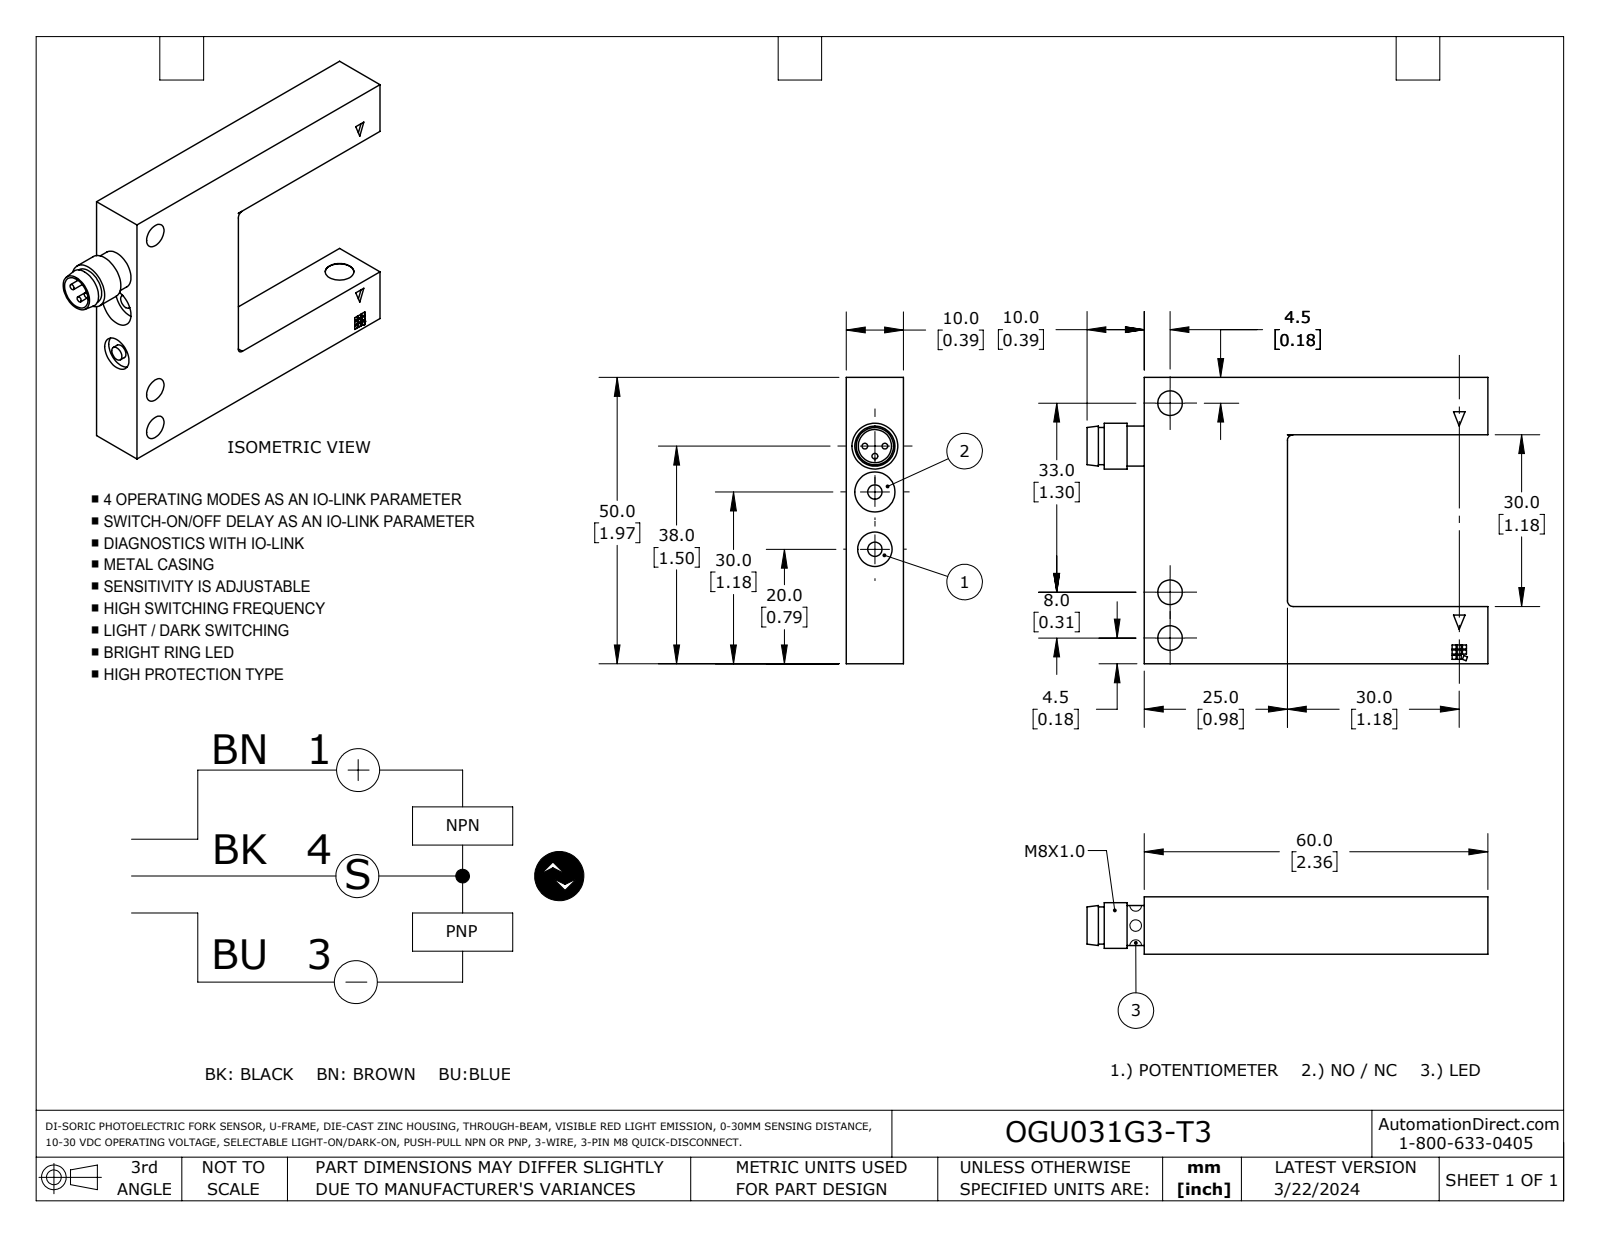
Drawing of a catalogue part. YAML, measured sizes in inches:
part_name: "OGU031G3-T3"
step_written_by: "SolidWorks 2023 (AUTOMOTIVE_DESIGN)"
units: inches
bodies: {solids: 1, faces: 112, planar: 91, cylindrical: 20, other: 1}
overall_size: [2.756, 1.969, 0.394]
volume: 1.173
surface_area: 11.85
round_holes:
  - {diameter: 0.169, count: 3}
  - {diameter: 0.118, count: 1}
  - {diameter: 0.197, count: 1}
  - {diameter: 0.228, count: 1}
  - {diameter: 0.236, count: 1}
  - {diameter: 0.276, count: 1}
round_bosses_or_shafts:
  - {diameter: 0.039, count: 3}
  - {diameter: 0.098, count: 2}
  - {diameter: 0.315, count: 1}
  - {diameter: 0.276, count: 1}
  - {diameter: 0.256, count: 1}
partial_cylinders:
  - {radius: 0.039, count: 3}
face_to_face_distances: [0.394, 1.575, 1.969, 1.181, 0.984, 1.378, 2.362, 0.392, 0.039, 1.577]
hole_center_spacings: [0.315, 0.394, 0.709, 1.299, 1.614]
